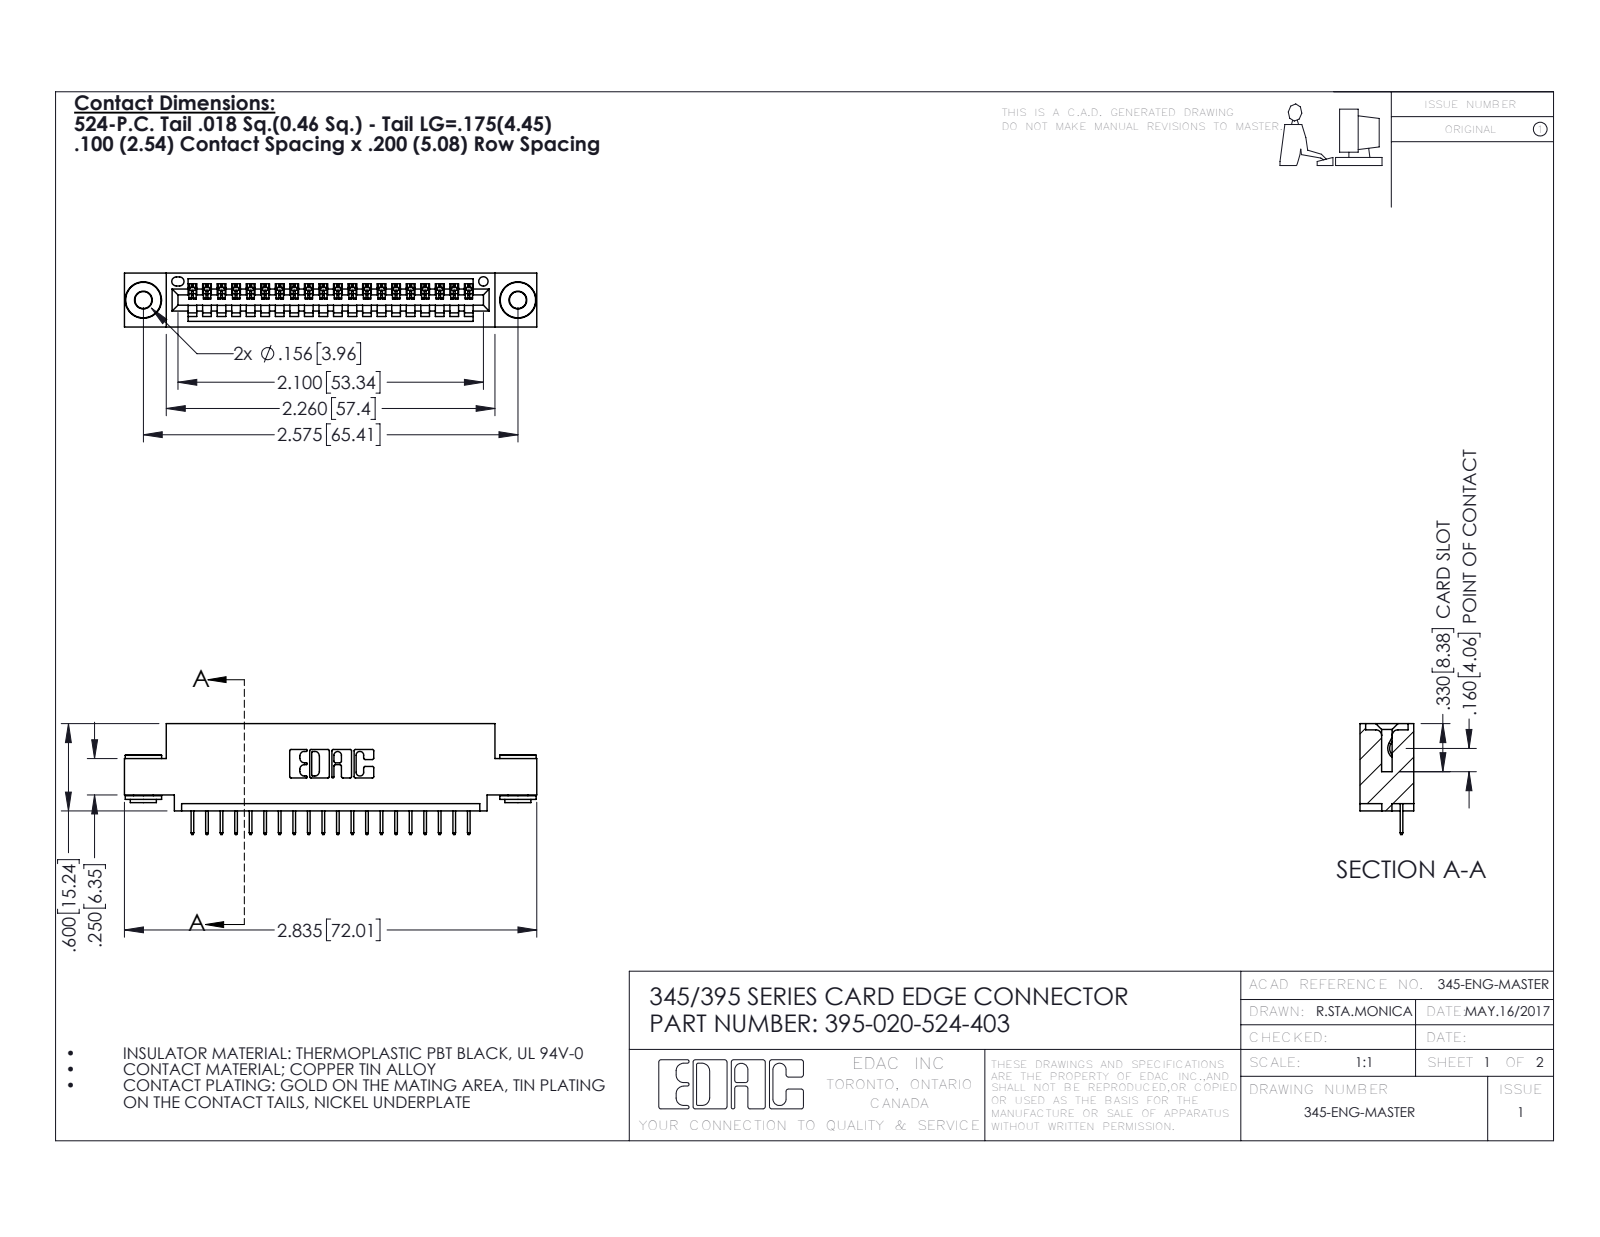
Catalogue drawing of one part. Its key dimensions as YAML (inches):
part_name: "395-020-524-403; 345-250-002_345-250-002-102; 345 Part_0.110 Offset - 0.156 Dia-TH; 345-292-001_345-293-124"
step_written_by: "SolidWorks 2016 (CONFIG_CONTROL_DESIGN)"
units: inches
bodies: {solids: 23, faces: 1408, planar: 1014, cylindrical: 386, other: 8}
overall_size: [2.835, 0.762, 0.37]
volume: 0.398
surface_area: 13.05
round_holes:
  - {diameter: 0.116, count: 2}
  - {diameter: 0.156, count: 2}
  - {diameter: 0.064, count: 1}
round_bosses_or_shafts:
  - {diameter: 0.25, count: 2}
  - {diameter: 0.18, count: 2}
  - {diameter: 0.136, count: 2}
partial_cylinders:
  - {radius: 0.006, count: 40}
  - {radius: 0.01, count: 22}
  - {radius: 0.007, count: 6}
  - {radius: 0.031, count: 6}
  - {radius: 0.026, count: 3}
  - {radius: 0.031, count: 2}
  - {radius: 0.04, count: 2}
  - {radius: 0.014, count: 1}
face_to_face_distances: [0.072, 0.298, 0.37, 0.2, 0.025, 0.098, 0.272, 0.225, 0.072, 0.149]
hole_center_spacings: [0.27, 2.341, 2.575]
